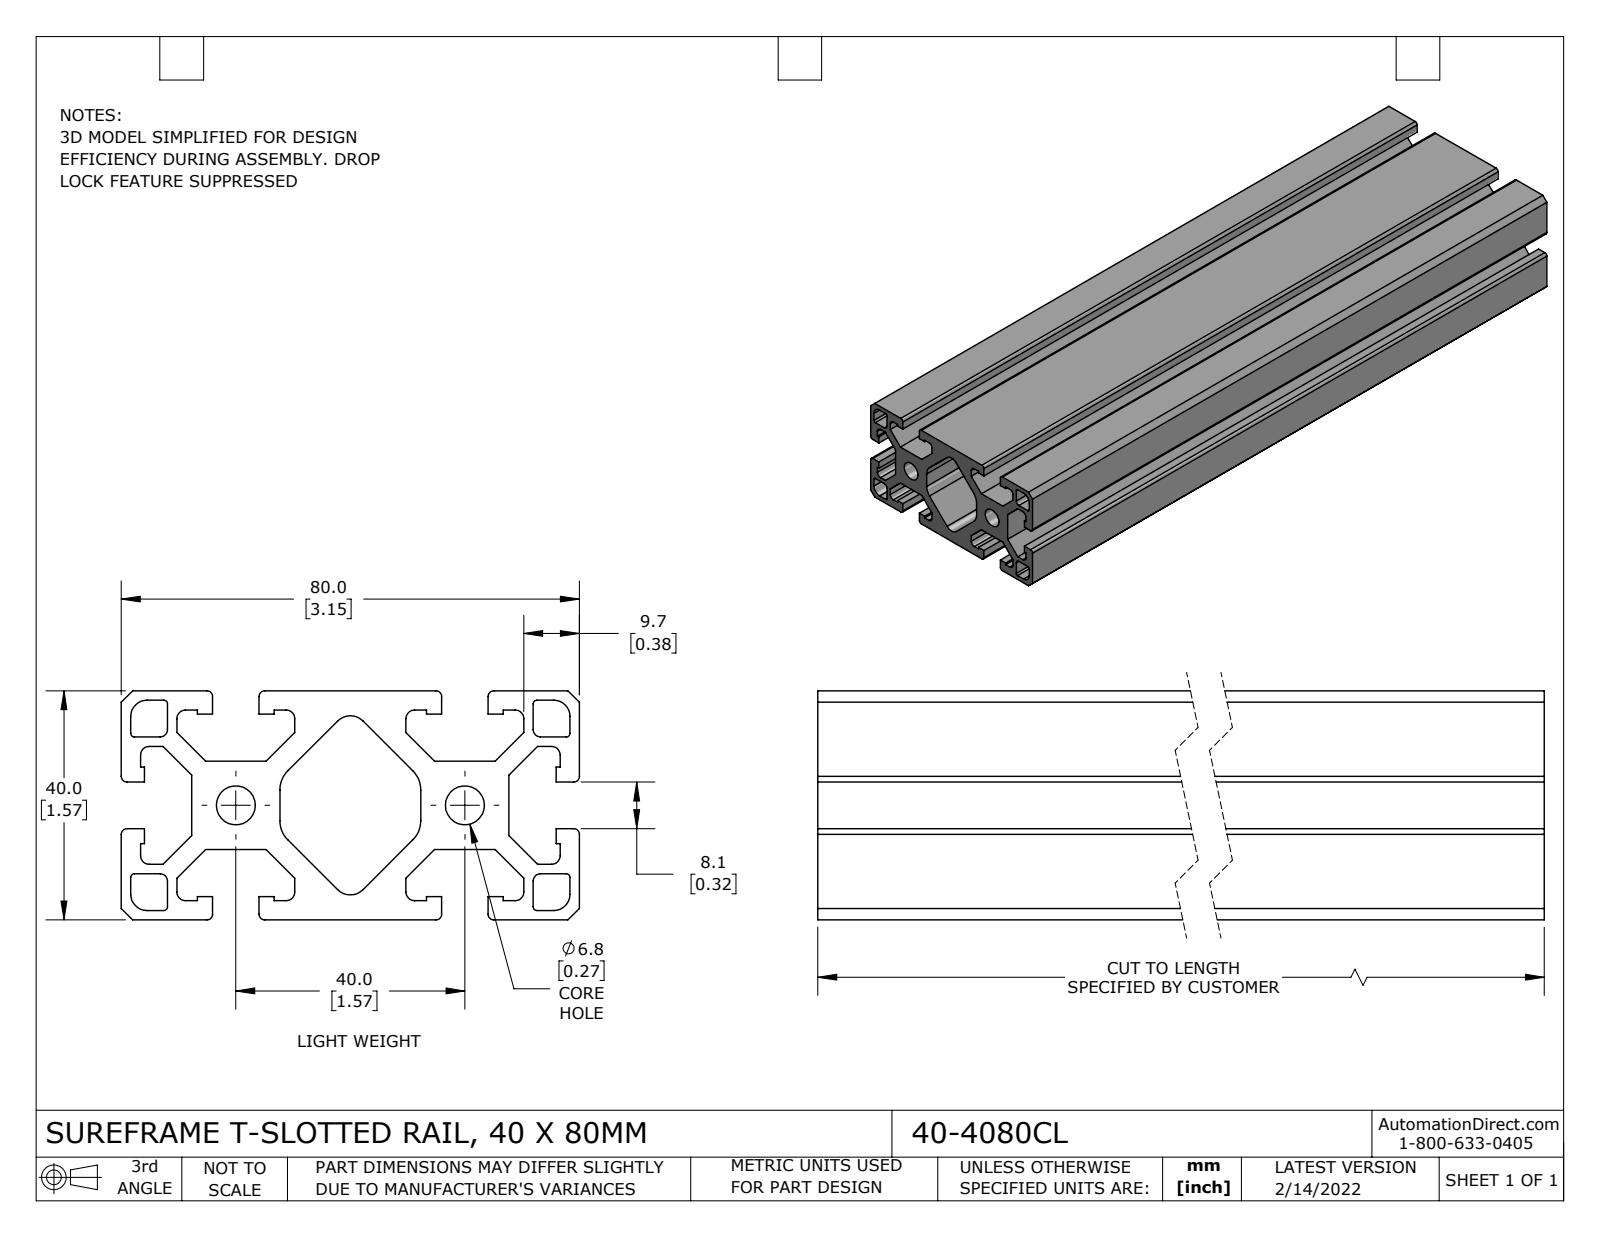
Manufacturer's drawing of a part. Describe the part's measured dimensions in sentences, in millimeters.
The part is named "40-4080CL". Its 3-D file was written by "SolidWorks 2021 (CONFIG_CONTROL_DESIGN)". It is 1 solid with 166 faces: 116 planar, 50 cylindrical and 0 other. Overall it measures 254 by 80 by 40 millimeters. Its volume is 342 238 cubic millimeters and its surface area 186 010 square millimeters. Round holes: 2 of diameter 6.81. Partial cylindrical surfaces (rounded edges, fillets, slot ends): 12 of radius 1, 12 of radius 1.5, 8 of radius 0.63, 4 of radius 1.27, 4 of radius 2.8, 4 of radius 4.75, 2 of radius 3.17. The main face-to-face distances are 40, 12.3, 27.7, 3.87, 27.83, 11.76, 3.64, 8.06, 15.4, 4.06. The hole center spacings are 40.
